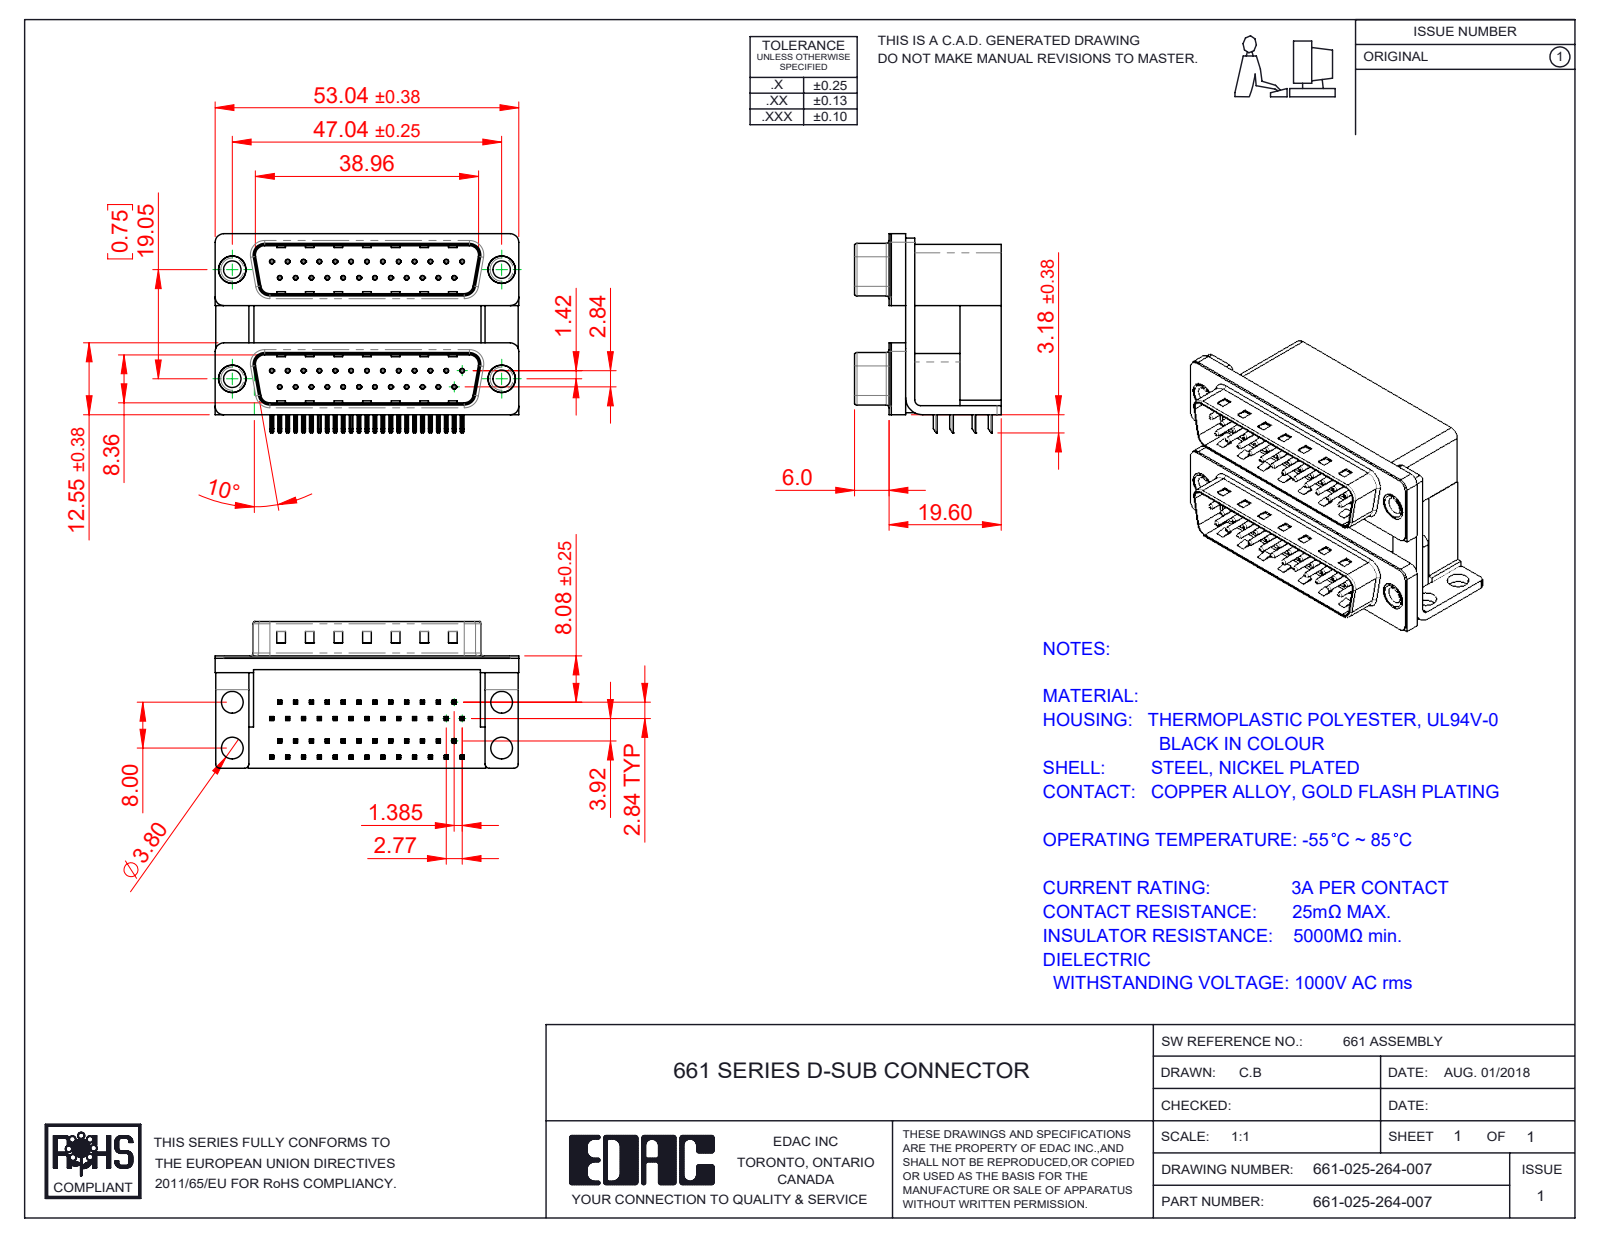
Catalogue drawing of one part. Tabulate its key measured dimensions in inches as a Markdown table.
| quantity | value |
| --- | --- |
| part name | 661-025-264-007; 661 Housing Upper_25 Contacts M; 661 Thru Hole Rivet; 661 Housing Spacer_25 Contacts M (+7 more) |
| STEP written by | SolidWorks 2020 (CONFIG_CONTROL_DESIGN) |
| units | inches |
| bodies | 61 solids, 4510 faces (2934 planar, 1230 cylindrical, 346 other) |
| overall size | 2.088 × 1.369 × 1.008 |
| volume | 1.281 in³ |
| surface area | 33.49 in² |
| round holes (diameter × count) | 0.014 × 50, 0.031 × 50, 0.12 × 4, 0.138 × 4, 0.157 × 4, 0.189 × 4, 0.197 × 4 |
| round bosses / shafts (diameter × count) | 0.03 × 50, 0.193 × 4, 0.187 × 4, 0.152 × 4 |
| partial cylindrical surfaces (radius × count) | 0.01 × 200, 0.005 × 100, 0.02 × 16, 0.059 × 14, 0.035 × 8, 0.063 × 8, 0.079 × 8, 0.016 × 4 |
| main face-to-face distances | 0.016, 0.756, 0.75, 0.283, 0.472, 0.421, 0.657, 0.374, 0.098, 0.329 |
| hole center spacings | 0.124, 0.109, 0.218, 0.327, 0.436, 0.545, 0.654, 0.198 |
